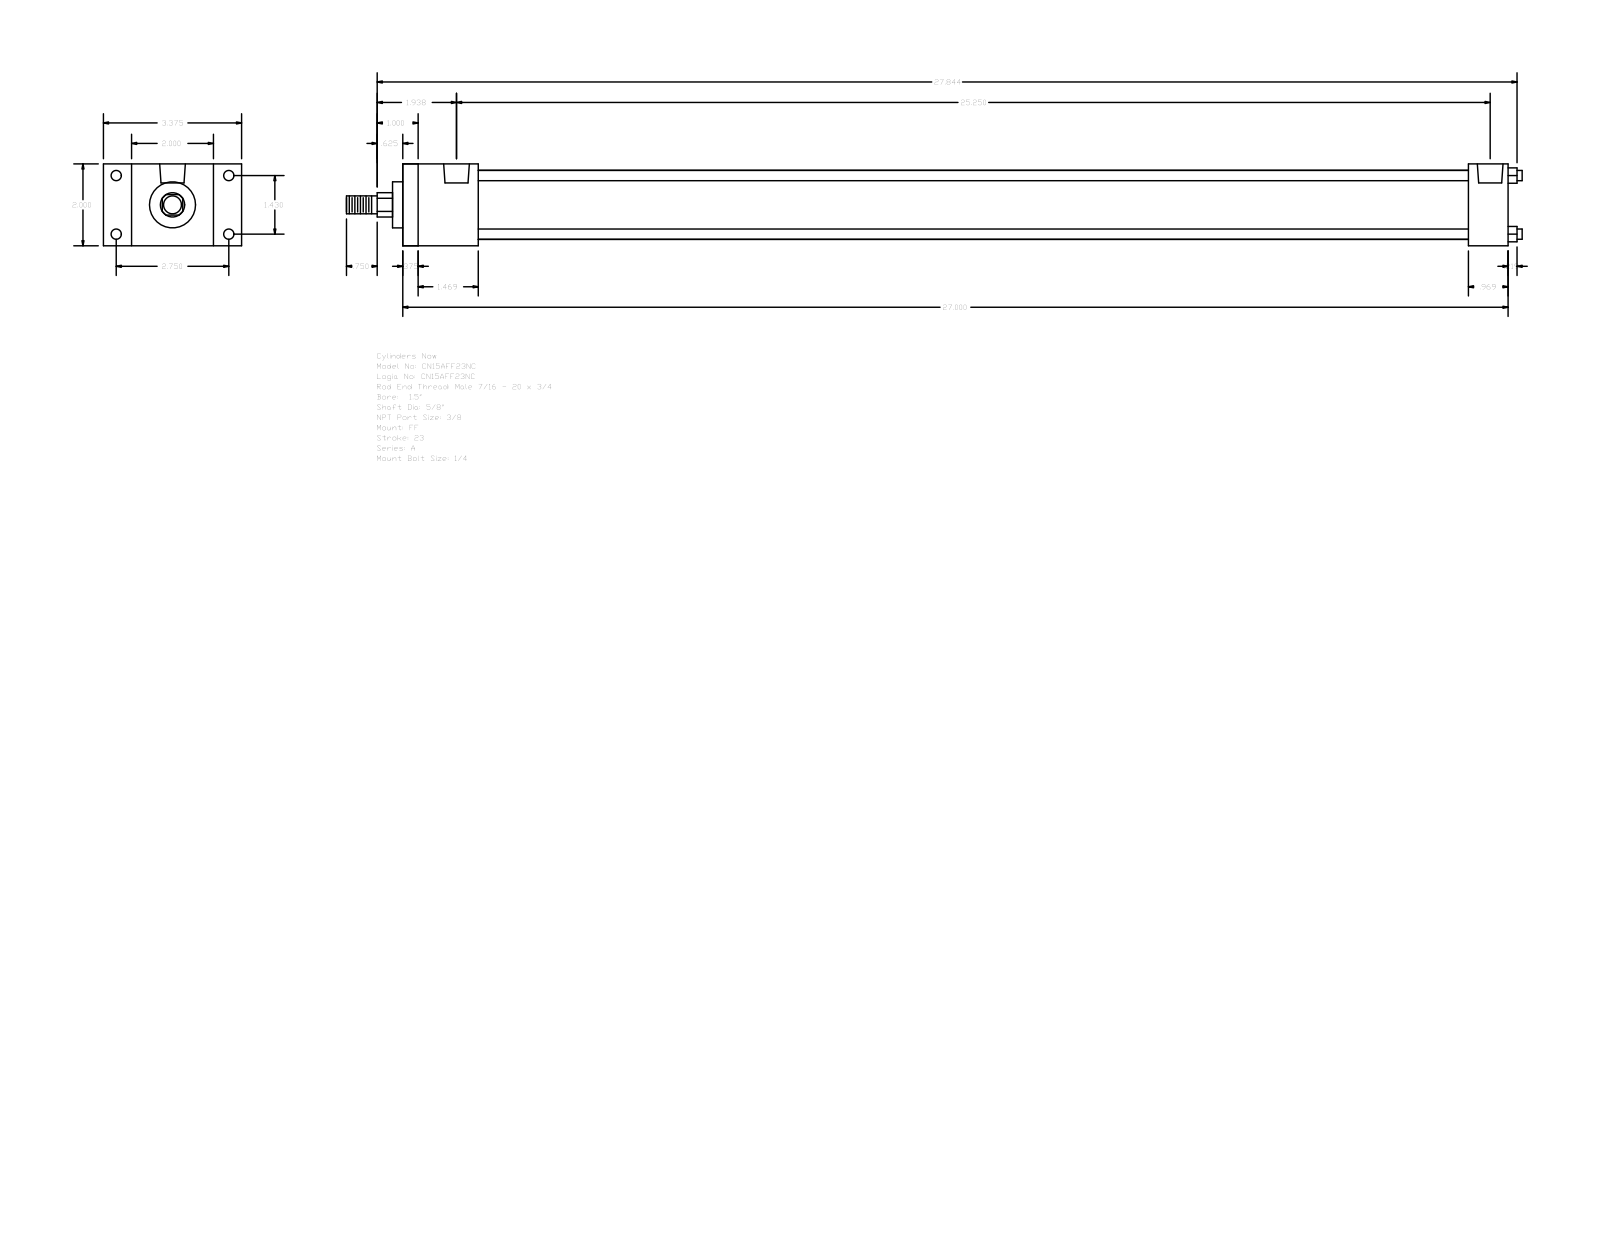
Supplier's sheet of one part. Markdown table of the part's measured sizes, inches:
| quantity | value |
| --- | --- |
| part name | A_FF__0150_0.625 |
| STEP written by | GSSL Pune (CONFIG_CONTROL_DESIGN) |
| units | inches |
| bodies | 0 solids, 92 faces (64 planar, 28 cylindrical, 0 other) |
| overall size | 28.719 × 3.375 × 2 |
| round holes (diameter × count) | 0.219 × 4, 0.25 × 4, 0.627 × 2 |
| round bosses / shafts (diameter × count) | 0.25 × 4, 1.69 × 1, 1.125 × 1, 0.625 × 1, 0.437 × 1 |
| partial cylindrical surfaces (radius × count) | 0.297 × 1 |
| main face-to-face distances | 2, 27, 0.375, 26.625, 1.844, 26.031, 1.469, 25.656, 24.187, 25.156 |
| hole center spacings | 0.156, 1.43, 2.75, 3.099, 24.937, 25.094, 25.25 |
